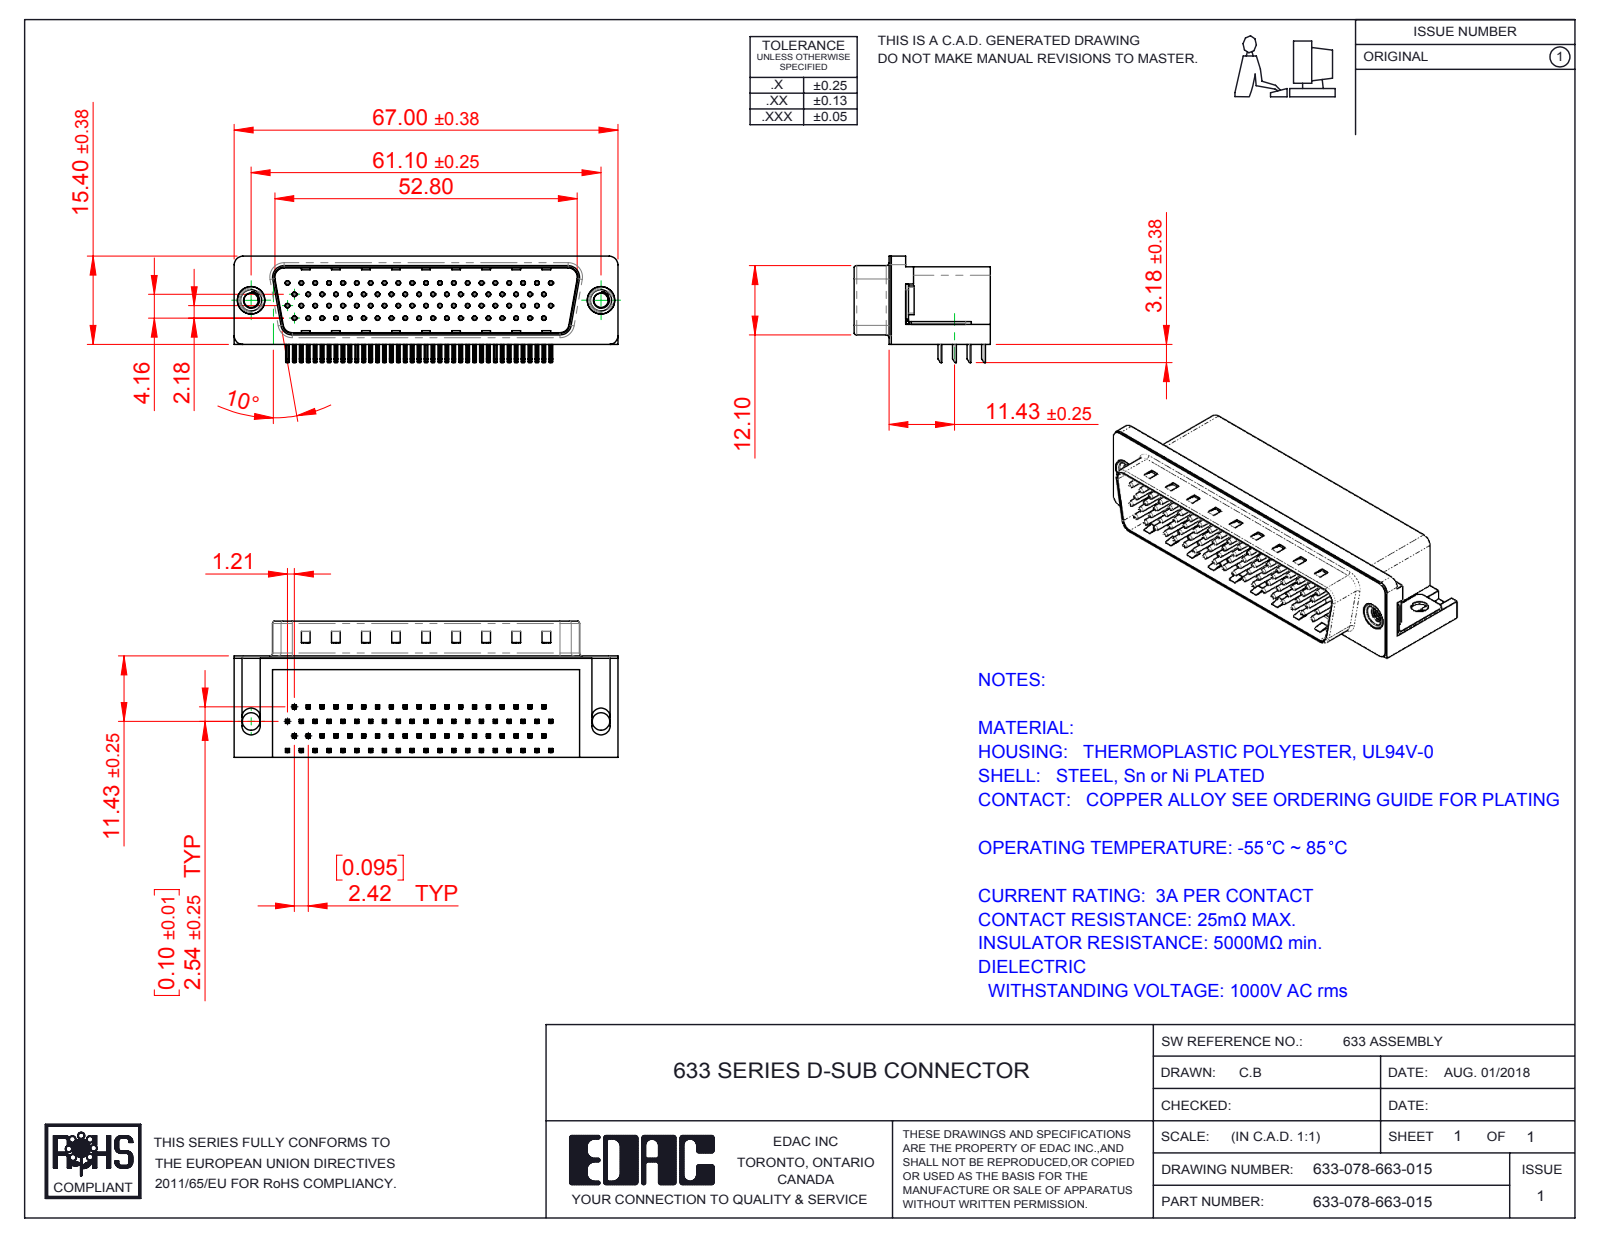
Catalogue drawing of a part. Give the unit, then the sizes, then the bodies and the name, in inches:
Units: inches
Overall size (bounding box): 2.638 × 0.937 × 0.731
Round holes (diameter × count): ⌀0.014 ×78, ⌀0.031 ×78, ⌀0.098 ×2, ⌀0.12 ×2, ⌀0.157 ×2, ⌀0.189 ×2, ⌀0.197 ×2
Round bosses / shafts (diameter × count): ⌀0.03 ×78, ⌀0.193 ×2, ⌀0.187 ×2, ⌀0.154 ×2
Partial cylindrical surfaces — rounded edges, fillets, slot ends (radius × count): R0.01 ×320, R0.005 ×156, R0.039 ×16, R0.02 ×9, R0.063 ×8, R0.059 ×6, R0.018 ×4, R0.035 ×4
Main face-to-face distances: 0.016, 0.52, 0.681, 0.461, 0.526, 0.081, 0.541, 0.065, 0.073, 0.469
Hole centre spacings: 0.095, 0.191, 0.286, 0.381, 0.246, 0.281, 0.476, 0.339
Volume: 0.891 in³ · Surface area: 25.33 in²
Bodies: 84 solids, 6274 faces (3979 planar, 1782 cylindrical, 513 other)
Part name (STEP PRODUCT): 633-078-663-015; 633 Contact Bottom_78 Contact; 633 Thru Hole Board Mount_78 Contact; 633 Contact Top 78 (+5 more)
STEP written by: SolidWorks 2016 (CONFIG_CONTROL_DESIGN)
